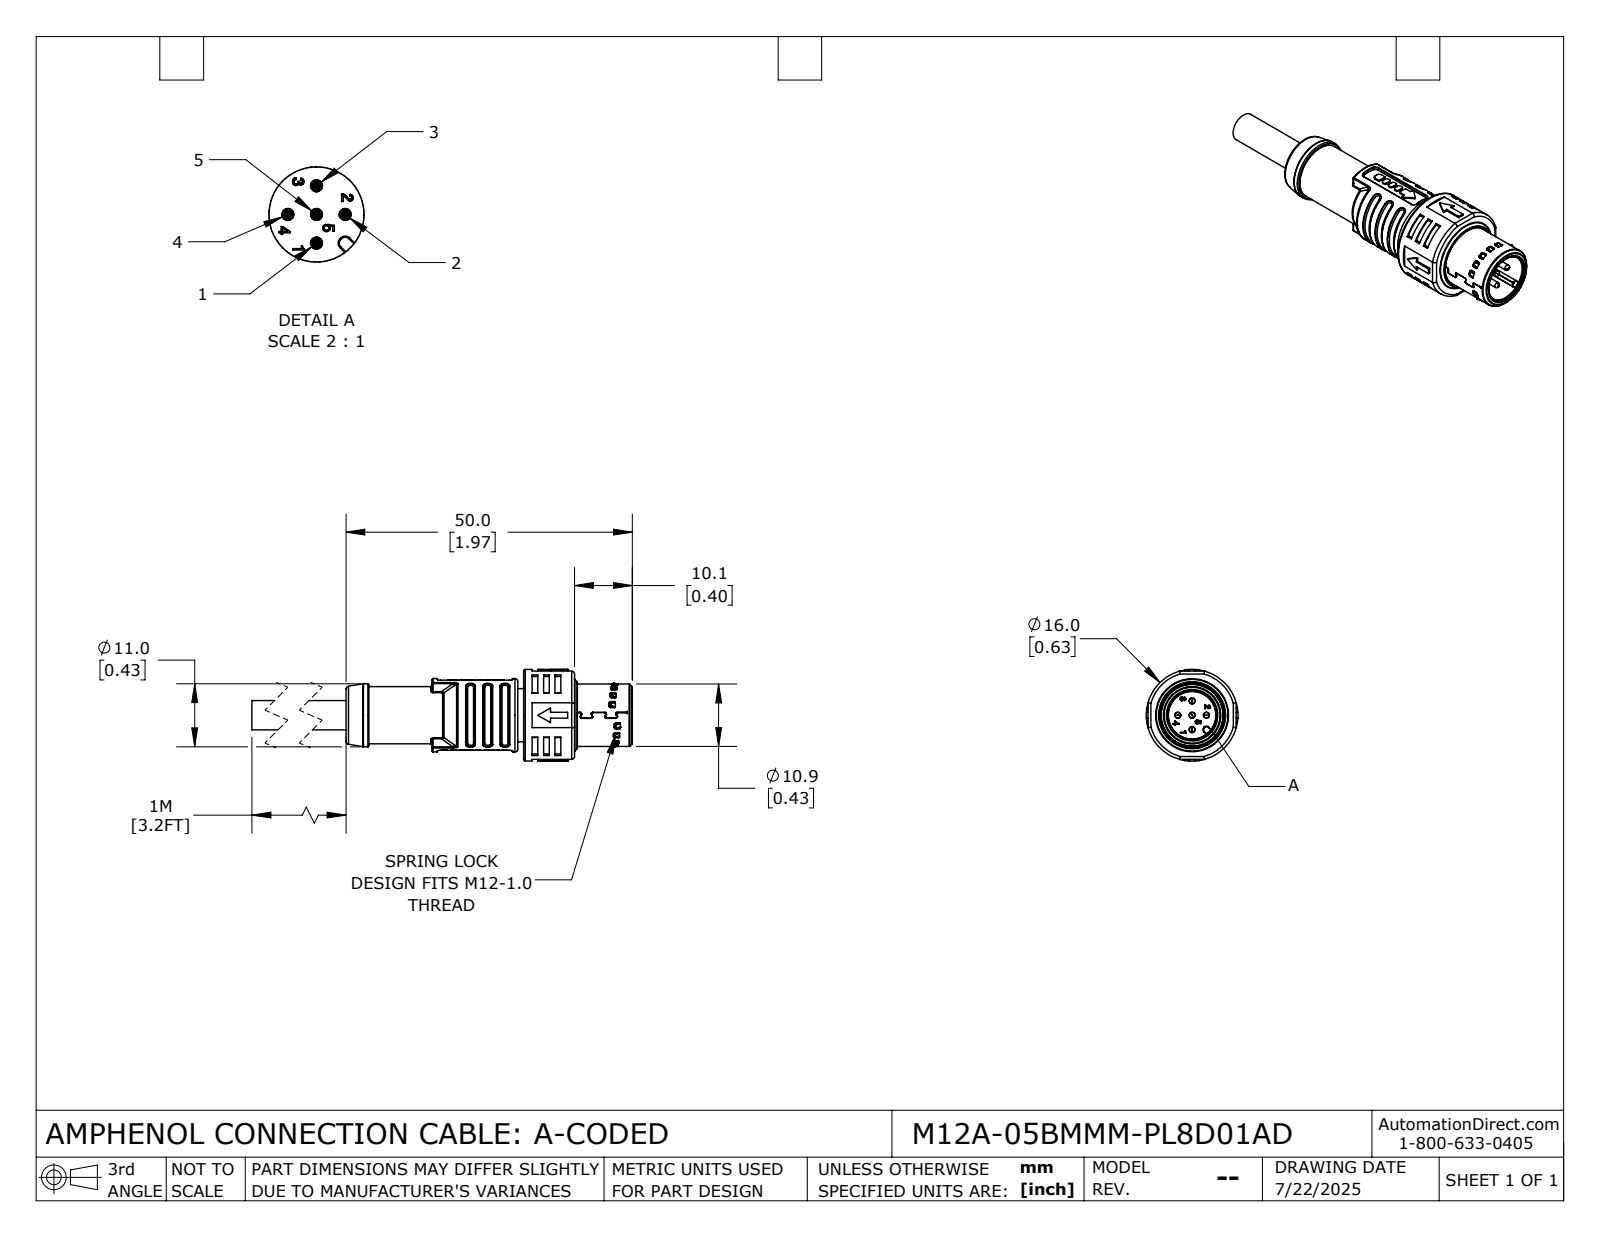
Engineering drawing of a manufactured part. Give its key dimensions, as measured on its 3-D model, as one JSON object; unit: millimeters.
{"part_name": "M12A-05BMMM-PL8D01AD", "step_written_by": "SolidWorks 2024 (CONFIG_CONTROL_DESIGN)", "units": "millimeters", "bodies": {"solids": 1, "faces": 2230, "planar": 1085, "cylindrical": 648, "other": 497}, "overall_size": [65, 16, 16], "volume_mm3": 5076, "surface_area_mm2": 5586, "round_holes": [[1.05, 5], [8.3, 1], [9, 1], [10.15, 1], [10.5, 1], [10.9, 1], [11.5, 1], [11.8, 1], [14.2, 1]], "round_bosses_or_shafts": [[1, 5], [16, 1], [14.1, 1], [12.8, 1], [12.4, 1], [11, 1], [10.45, 1], [10.4, 1]], "partial_cylinders_radius": [[0.2, 114], [0.25, 66], [0.3, 64], [0.15, 44], [0.5, 38], [0.13, 12], [0.7, 11], [0.1, 10]], "face_to_face_distances": [1, 10.1, 8.9, 8.6, 2.5, 30, 1.5, 1.2, 32.5, 15.4], "hole_center_spacings": [2.5, 3.54, 5]}
